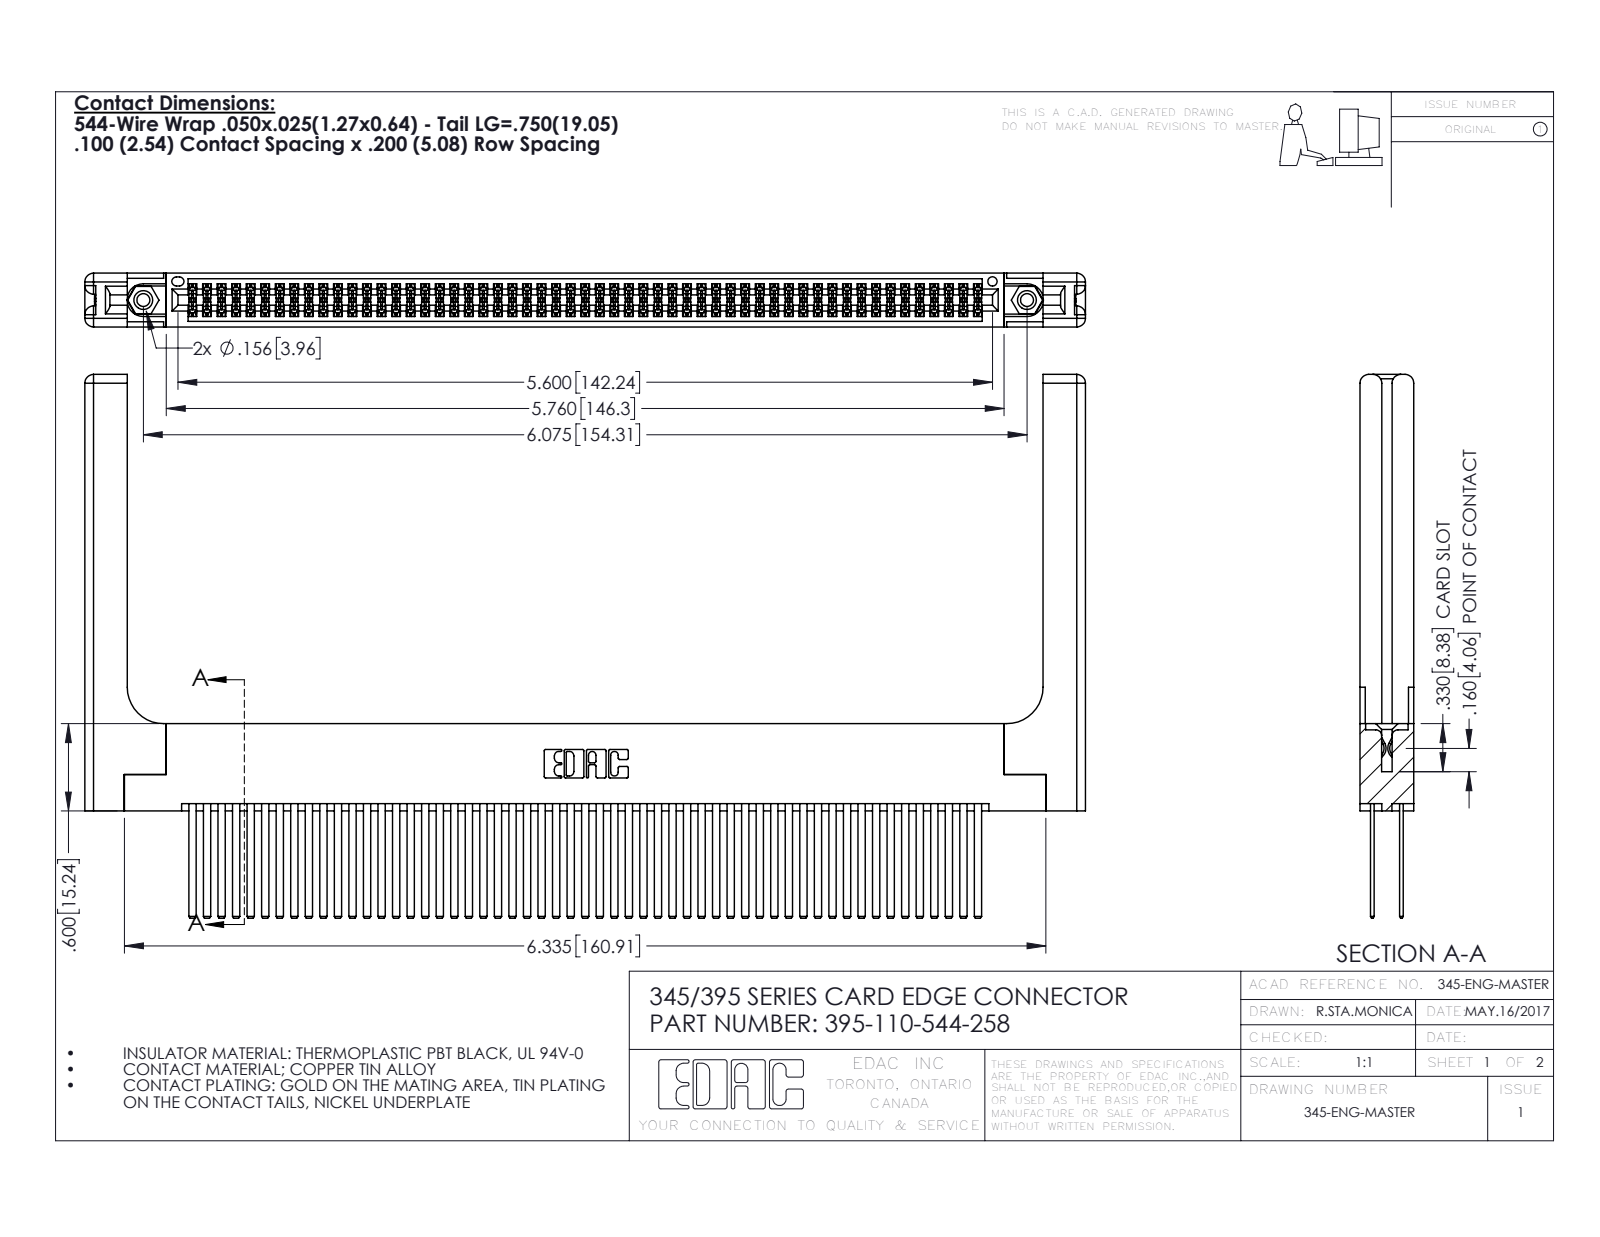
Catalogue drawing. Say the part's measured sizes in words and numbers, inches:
The part is named "345-292-001_345-293-144; 345-250-001_345-250-001-102; 345-220-058_345-220-058; 395-110-544-258 (+1 more)". Its 3-D file was written by "SolidWorks 2016 (CONFIG_CONTROL_DESIGN)". It is 115 solids with 5222 faces: 3418 planar, 1744 cylindrical and 60 other. Overall it measures 6.879 by 3.737 by 0.37 inches. Its volume is 1.654 cubic inches and its surface area 57.93 square inches. Round holes: 2 of diameter 0.089, 2 of diameter 0.125, 2 of diameter 0.156, 1 of diameter 0.064. Round bosses or shafts: 2 of diameter 0.155. Partial cylindrical surfaces (rounded edges, fillets, slot ends): 165 of radius 0.006, 22 of radius 0.01, 16 of radius 0.06, 6 of radius 0.007, 6 of radius 0.031, 3 of radius 0.026, 2 of radius 0.014, 2 of radius 0.019. The main face-to-face distances are 0.072, 0.298, 0.2, 0.098, 0.272, 0.025, 0.37, 0.225, 0.175, 0.148. The hole center spacings are 0.27, 5.839, 6.075.
